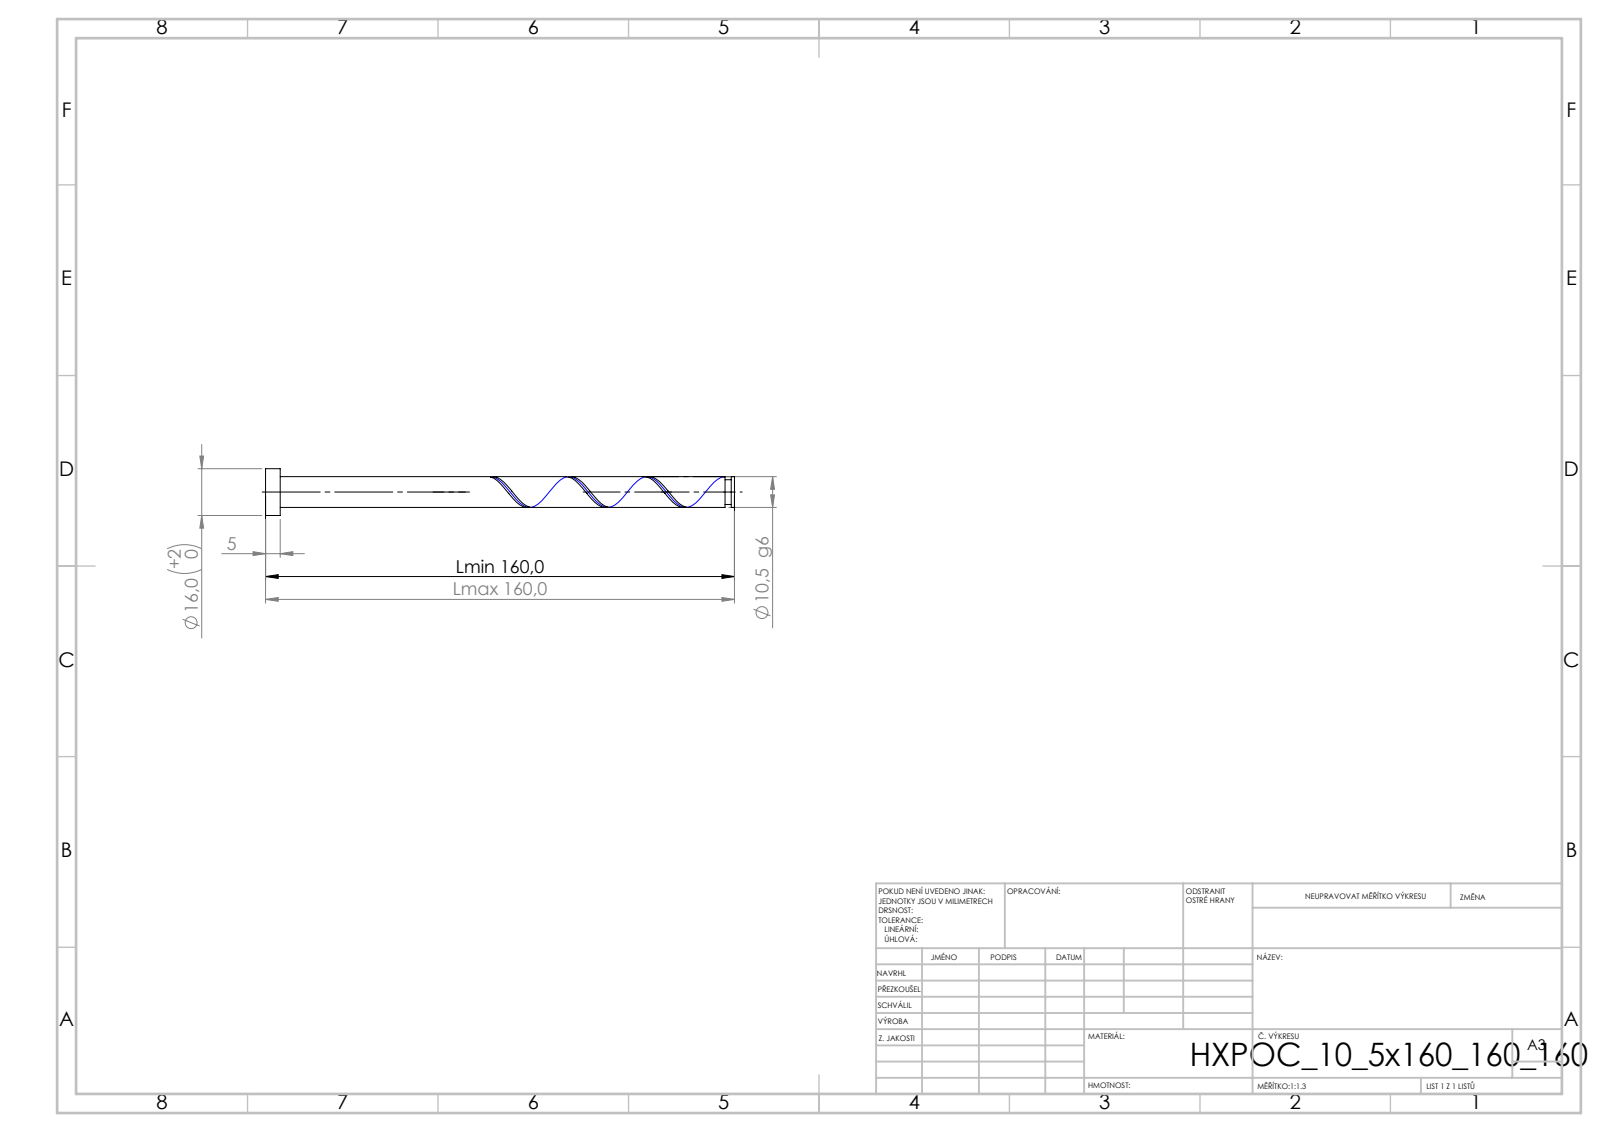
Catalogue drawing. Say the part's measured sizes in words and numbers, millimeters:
Its 3-D file was written by "SolidWorks 2019 (CONFIG_CONTROL_DESIGN)". It is 1 solid with 21 faces: 6 planar, 14 cylindrical and 1 other. Overall it measures 160 by 16 by 16 millimeters. Its volume is 14 229 cubic millimeters and its surface area 5 966 square millimeters. Round bosses or shafts: 1 of diameter 16, 1 of diameter 10.5, 1 of diameter 8.4. The main face-to-face distances are 5, 160, 155, 158.87, 153.87, 1.13, 156.77, 151.77, 2.1, 3.23.
